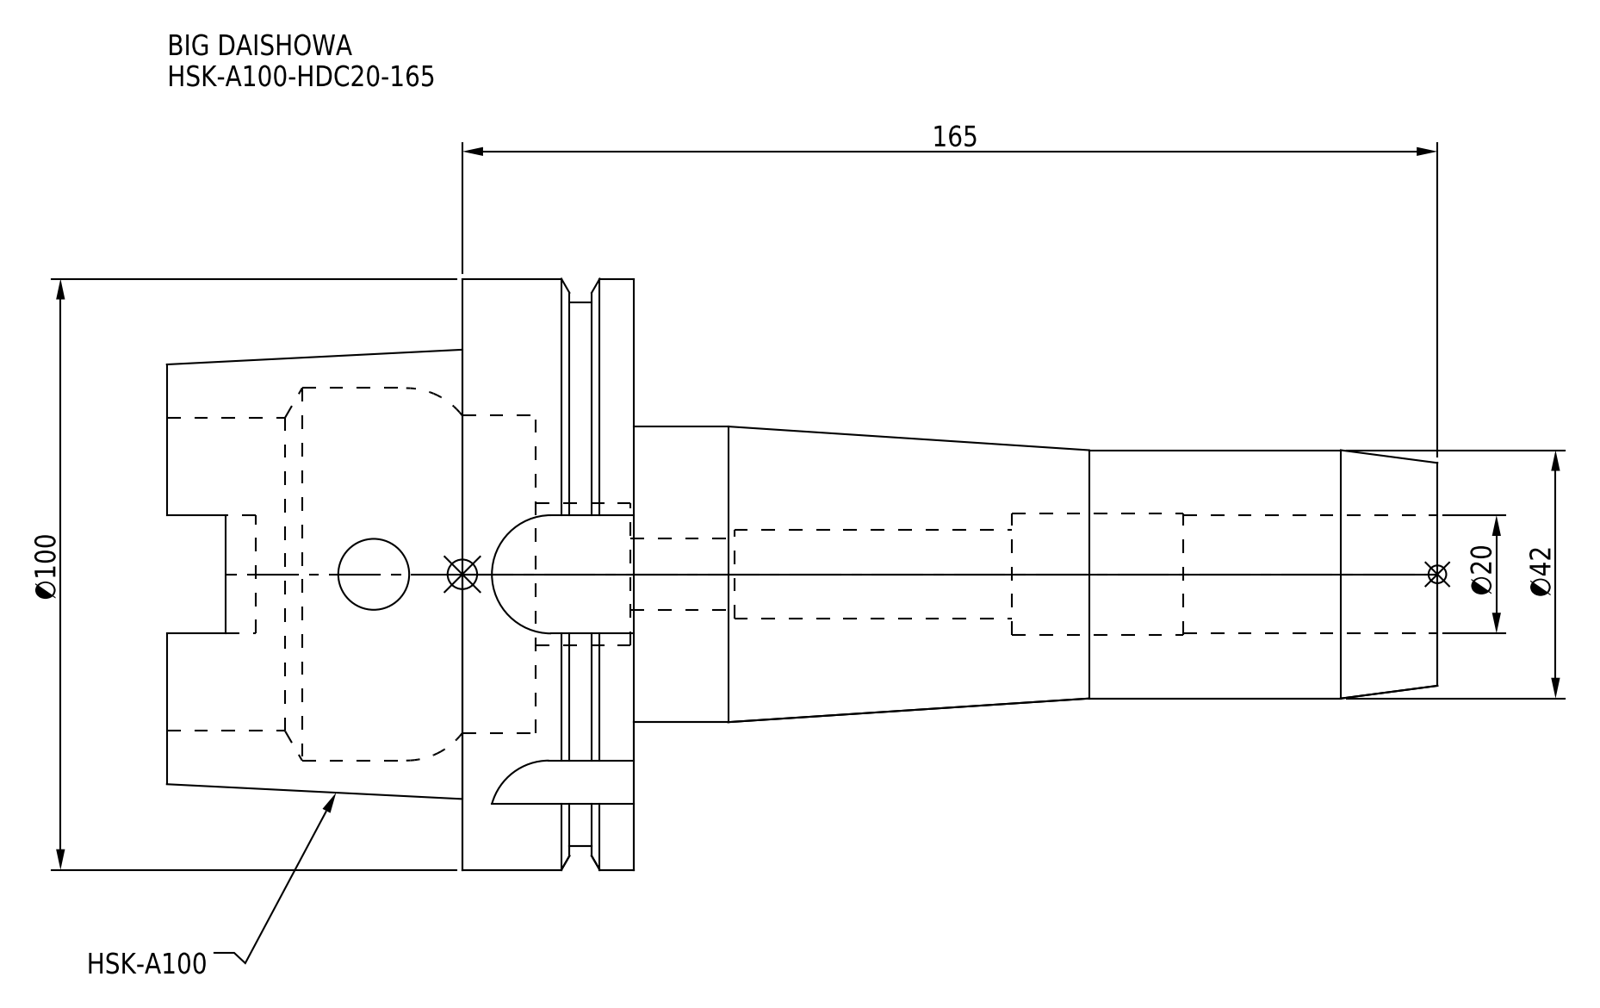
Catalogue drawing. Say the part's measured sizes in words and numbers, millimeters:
The part is named "HSK-A100-HDC20-165". Its 3-D file was written by "CREO PARAMETRIC BY PTC INC, 2016380 (AUTOMOTIVE_DESIGN)". It is 1 solid with 95 faces: 35 planar, 42 cylindrical and 18 other. Overall it measures 215 by 100 by 100 millimeters. Its volume is 432 687 cubic millimeters and its surface area 75 438 square millimeters. Round holes: 2 of diameter 12, 1 of diameter 15, 1 of diameter 20, 1 of diameter 20.5, 1 of diameter 24, 1 of diameter 53, 1 of diameter 53.8, 1 of diameter 63. Round bosses or shafts: 1 of diameter 100, 1 of diameter 92, 1 of diameter 50, 1 of diameter 42. Partial cylindrical surfaces (rounded edges, fillets, slot ends): 4 of radius 4.88, 4 of radius 10. The main face-to-face distances are 29, 16.55, 12.45, 79, 62.45, 50, 136, 152.55, 165, 215.
